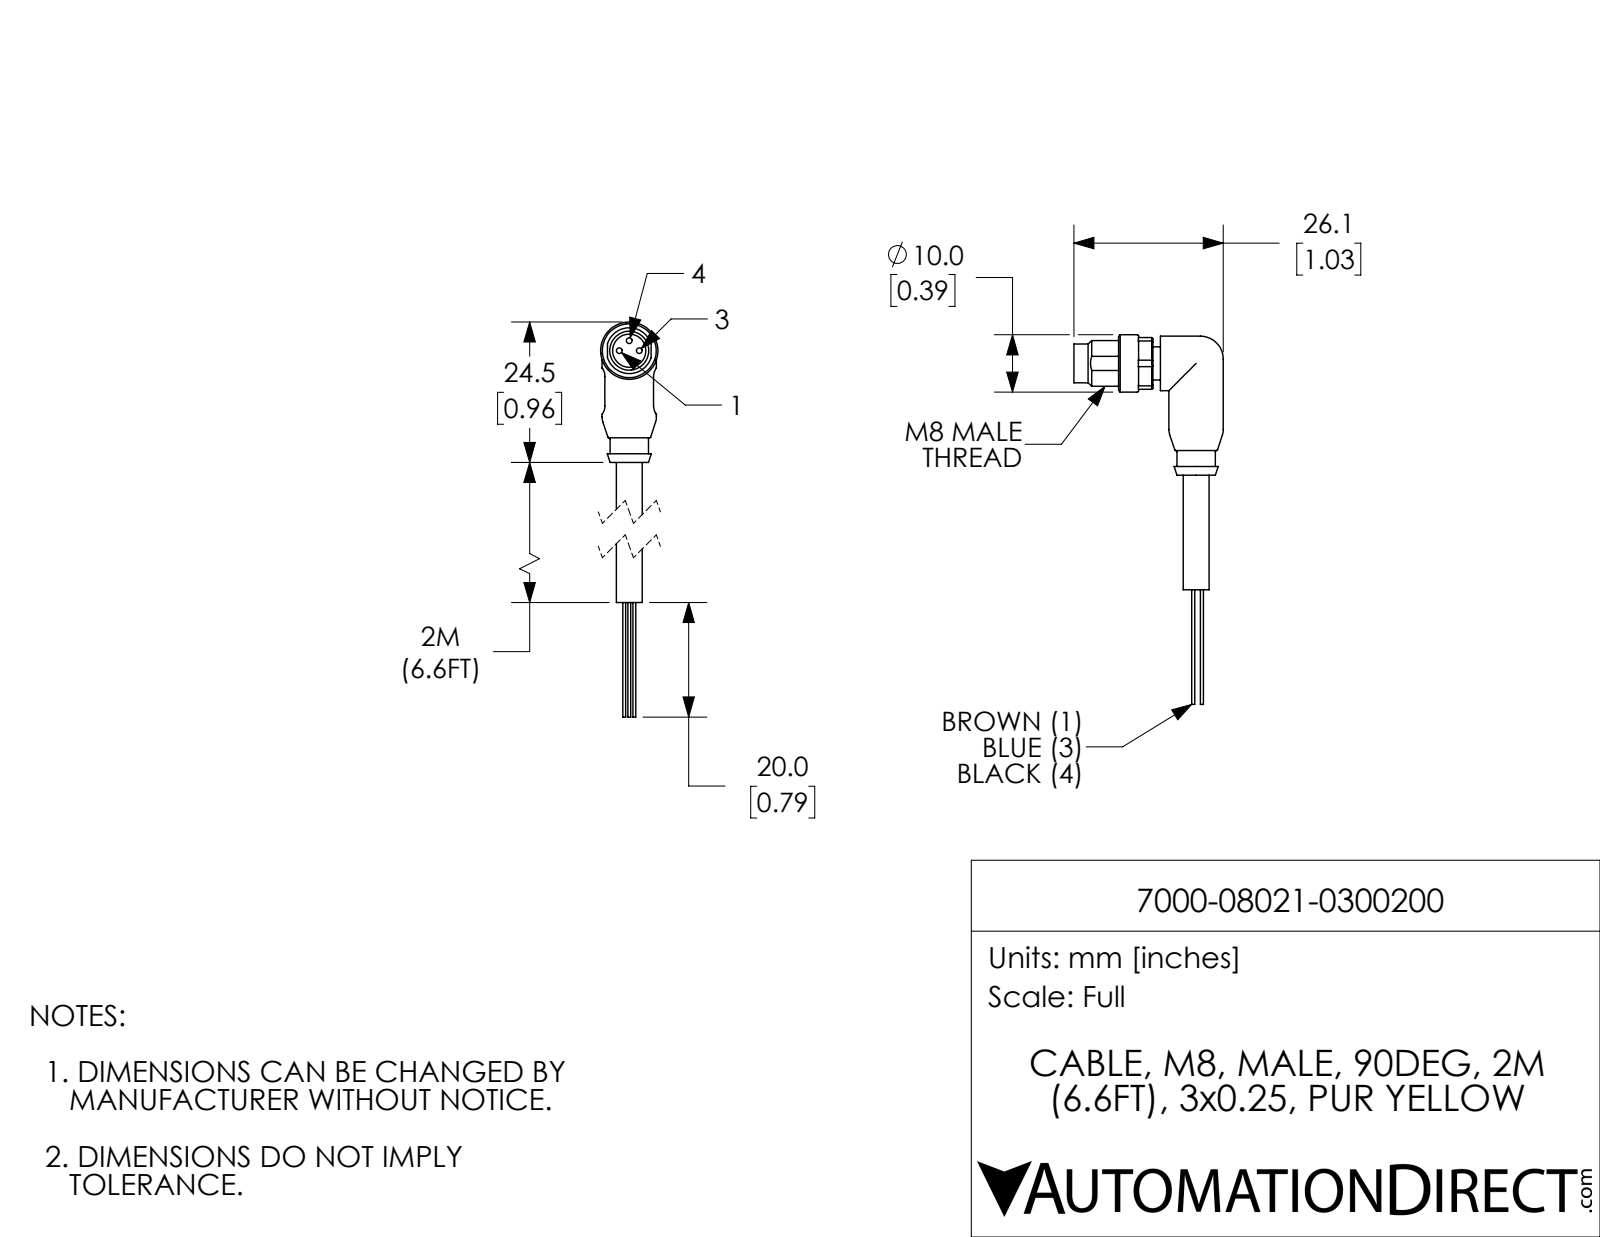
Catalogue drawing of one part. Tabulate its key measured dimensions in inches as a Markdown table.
| quantity | value |
| --- | --- |
| part name | 7000-08021-0300200 |
| STEP written by | SolidWorks 2021 (CONFIG_CONTROL_DESIGN) |
| units | inches |
| bodies | 4 solids, 118 faces (40 planar, 45 cylindrical, 33 other) |
| overall size | 2.539 × 1.028 × 0.394 |
| volume | 0.161 in³ |
| surface area | 2.831 in² |
| round holes (diameter × count) | 0.228 × 1 |
| round bosses / shafts (diameter × count) | 0.039 × 3, 0.02 × 3, 0.374 × 2, 0.394 × 1, 0.315 × 1, 0.268 × 1, 0.264 × 1, 0.177 × 1 |
| partial cylindrical surfaces (radius × count) | 0.008 × 4, 0.098 × 4, 0.193 × 1 |
| main face-to-face distances | 0.051, 0.354, 0.018, 0.317, 0.346, 0.398, 0.335, 0.11, 0.236, 0.287 |
